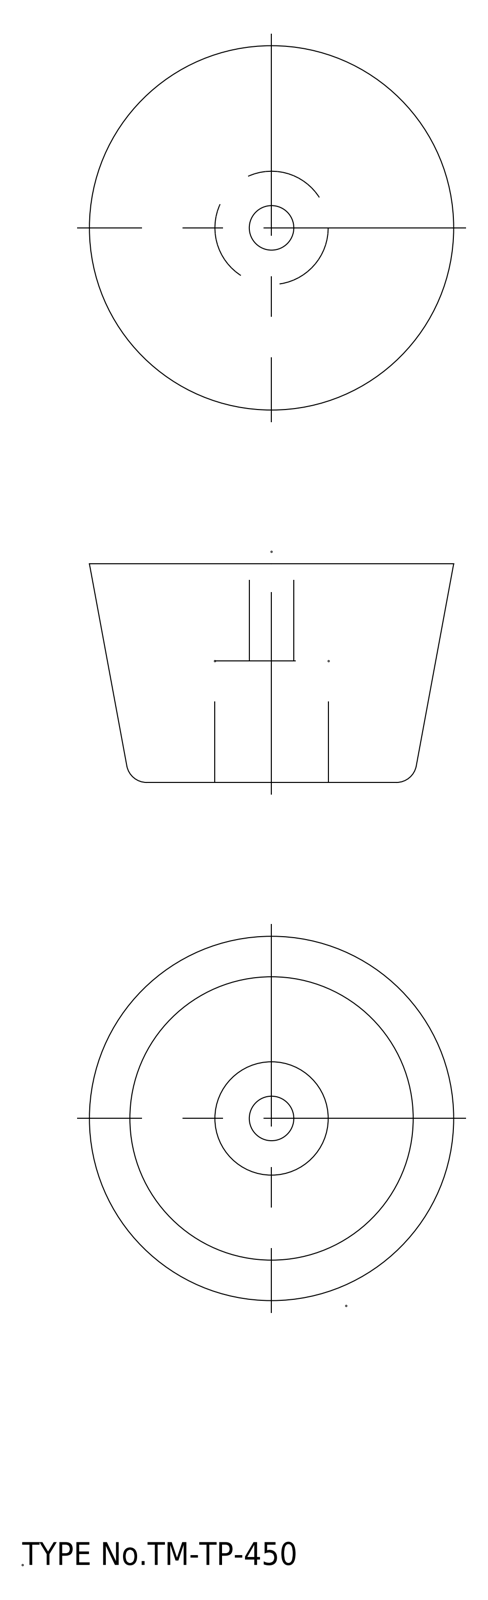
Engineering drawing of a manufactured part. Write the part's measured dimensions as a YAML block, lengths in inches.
step_written_by: "spGate 19.8.4 (****-****-****-****) (AUTOMOTIVE_DESIGN)"
units: inches
bodies: {solids: 1, faces: 11, planar: 3, cylindrical: 4, other: 4}
overall_size: [1.772, 1.772, 1.063]
volume: 1.921
surface_area: 10.46
round_holes:
  - {diameter: 0.217, count: 1}
  - {diameter: 0.551, count: 1}
face_to_face_distances: [1.063, 0.591, 0.472]
